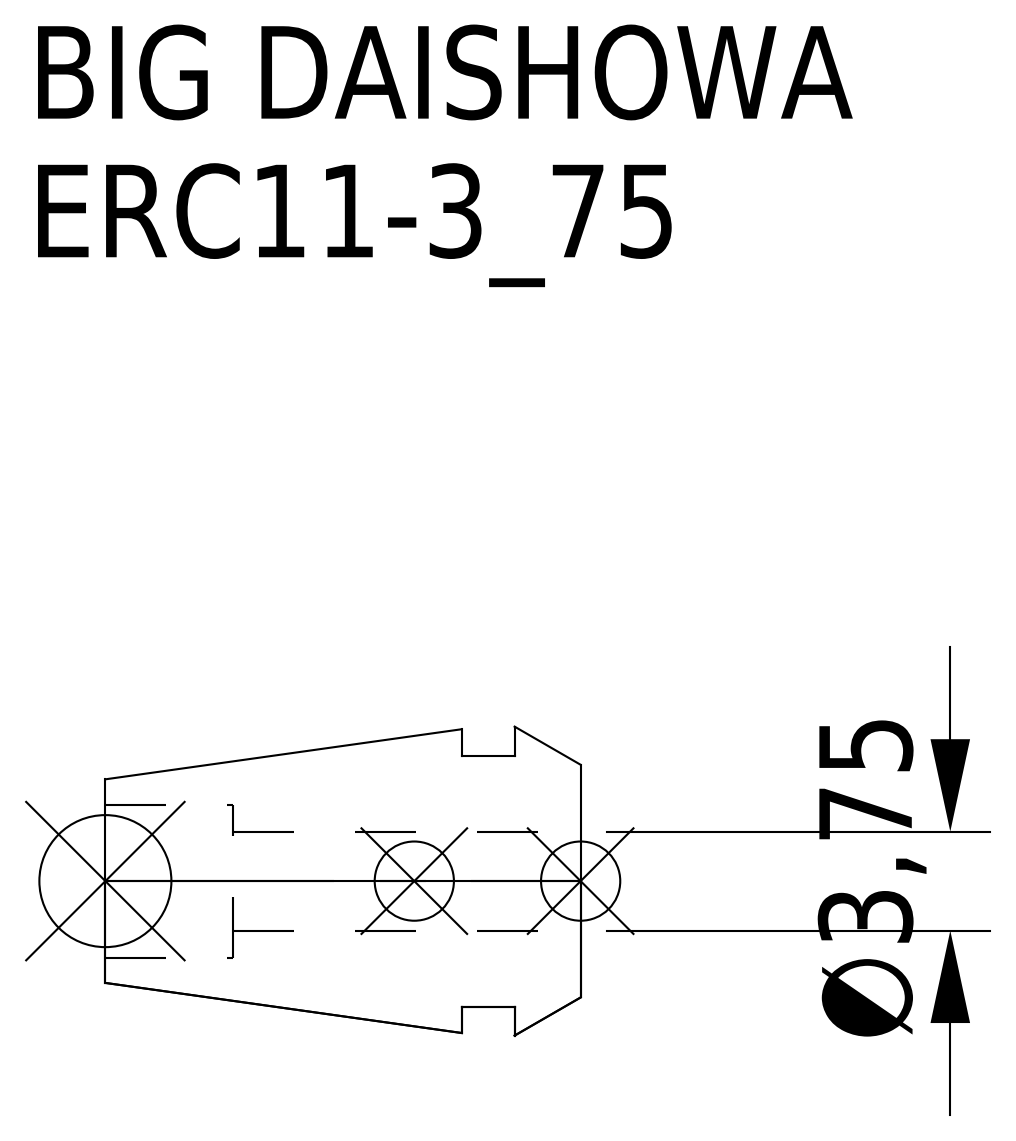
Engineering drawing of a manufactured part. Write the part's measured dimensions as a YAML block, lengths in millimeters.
part_name: "ERC11-3_75"
step_written_by: "CREO PARAMETRIC BY PTC INC, 2016380 (AUTOMOTIVE_DESIGN)"
units: millimeters
bodies: {solids: 1, faces: 15, planar: 5, cylindrical: 6, other: 4}
overall_size: [18, 11.7, 11.7]
volume: 1068
surface_area: 963
round_holes:
  - {diameter: 3.75, count: 1}
  - {diameter: 5.8, count: 1}
round_bosses_or_shafts:
  - {diameter: 9.5, count: 1}
face_to_face_distances: [2.5, 4.5, 2, 18, 15.5, 13.5, 13.15, 10.65, 8.65, 4.85]
